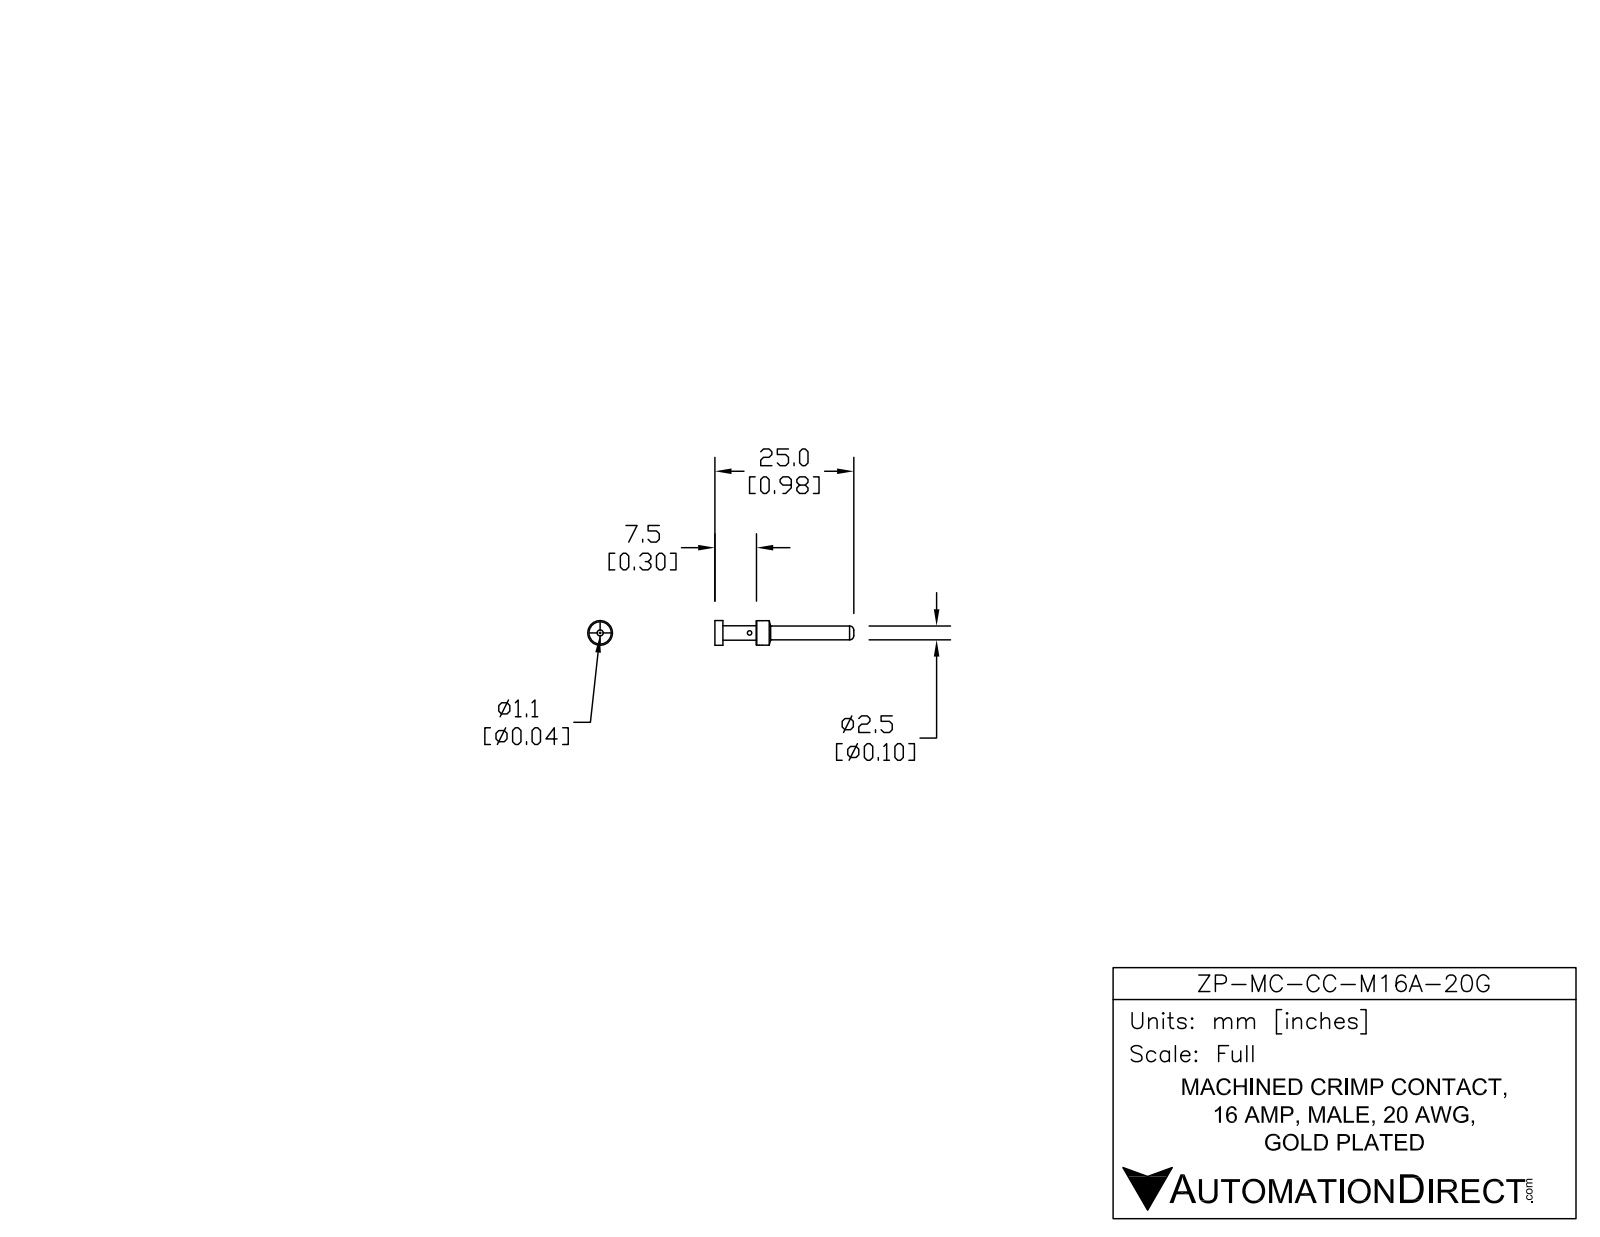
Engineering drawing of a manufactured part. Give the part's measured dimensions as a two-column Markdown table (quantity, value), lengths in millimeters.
| quantity | value |
| --- | --- |
| part name | ZP-MC-CC-M16A-20G |
| STEP written by | SolidWorks 2014 (AUTOMOTIVE_DESIGN) |
| units | millimeters |
| bodies | 1 solid, 24 faces (4 planar, 12 cylindrical, 8 other) |
| overall size | 25 × 4.48 × 4.48 |
| volume | 151 mm³ |
| surface area | 301 mm² |
| round holes (diameter × count) | 0.8 × 1, 1.1 × 1 |
| round bosses / shafts (diameter × count) | 4.48 × 1, 2.59 × 1, 2.5 × 1 |
| main face-to-face distances | 7.5, 2, 9.5, 15.5, 17.5, 25 |
